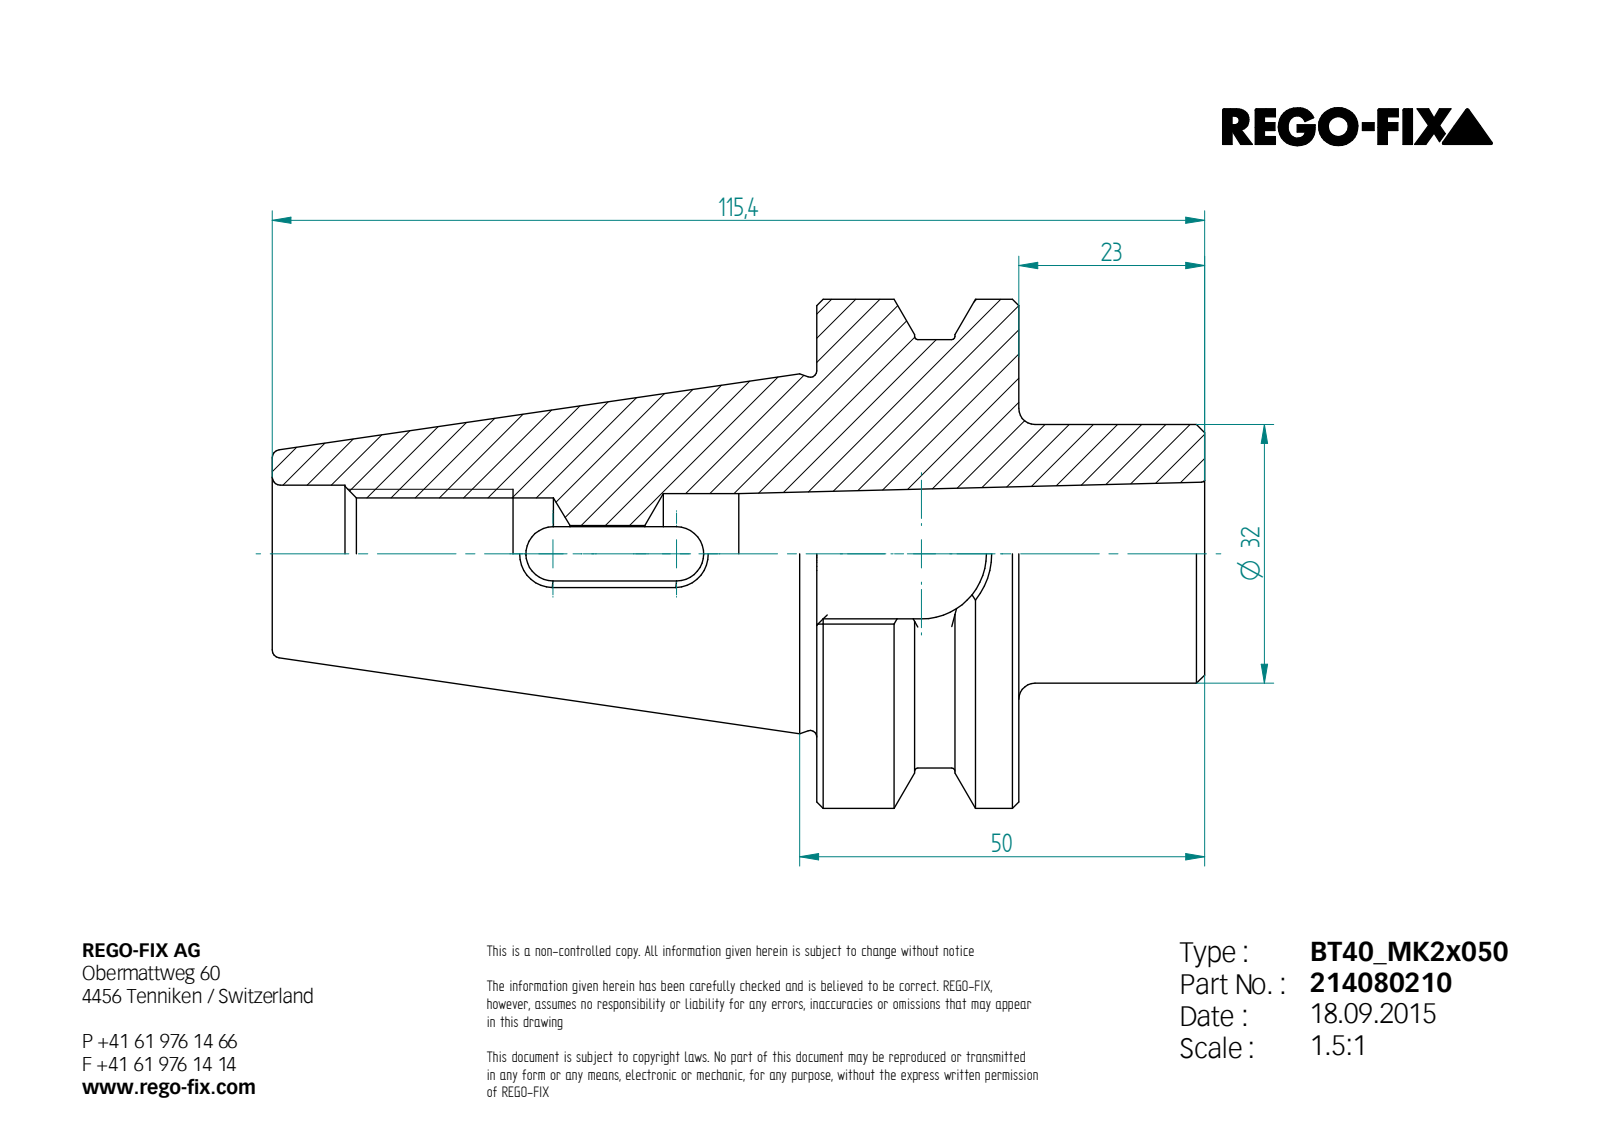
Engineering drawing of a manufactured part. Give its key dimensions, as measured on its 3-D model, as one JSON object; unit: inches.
{"step_written_by": "Unknown (AUTOMOTIVE_DESIGN)", "units": "inches", "bodies": {"solids": 1, "faces": 99, "planar": 40, "cylindrical": 22, "other": 37}, "overall_size": [4.543, 2.48, 2.48], "volume_in3": 7.85, "surface_area_in2": 41.05, "round_holes": [[0.545, 1], [0.587, 1], [0.669, 1]], "round_bosses_or_shafts": [[2.48, 1], [2.087, 1], [1.26, 1]], "partial_cylinders_radius": [[0.02, 4], [0.132, 2], [0.138, 1], [0.317, 1]], "face_to_face_distances": [0.984, 0.264, 1.89, 0.906, 0.185, 0.449, 1.776, 2.654, 3.638, 4.543]}
